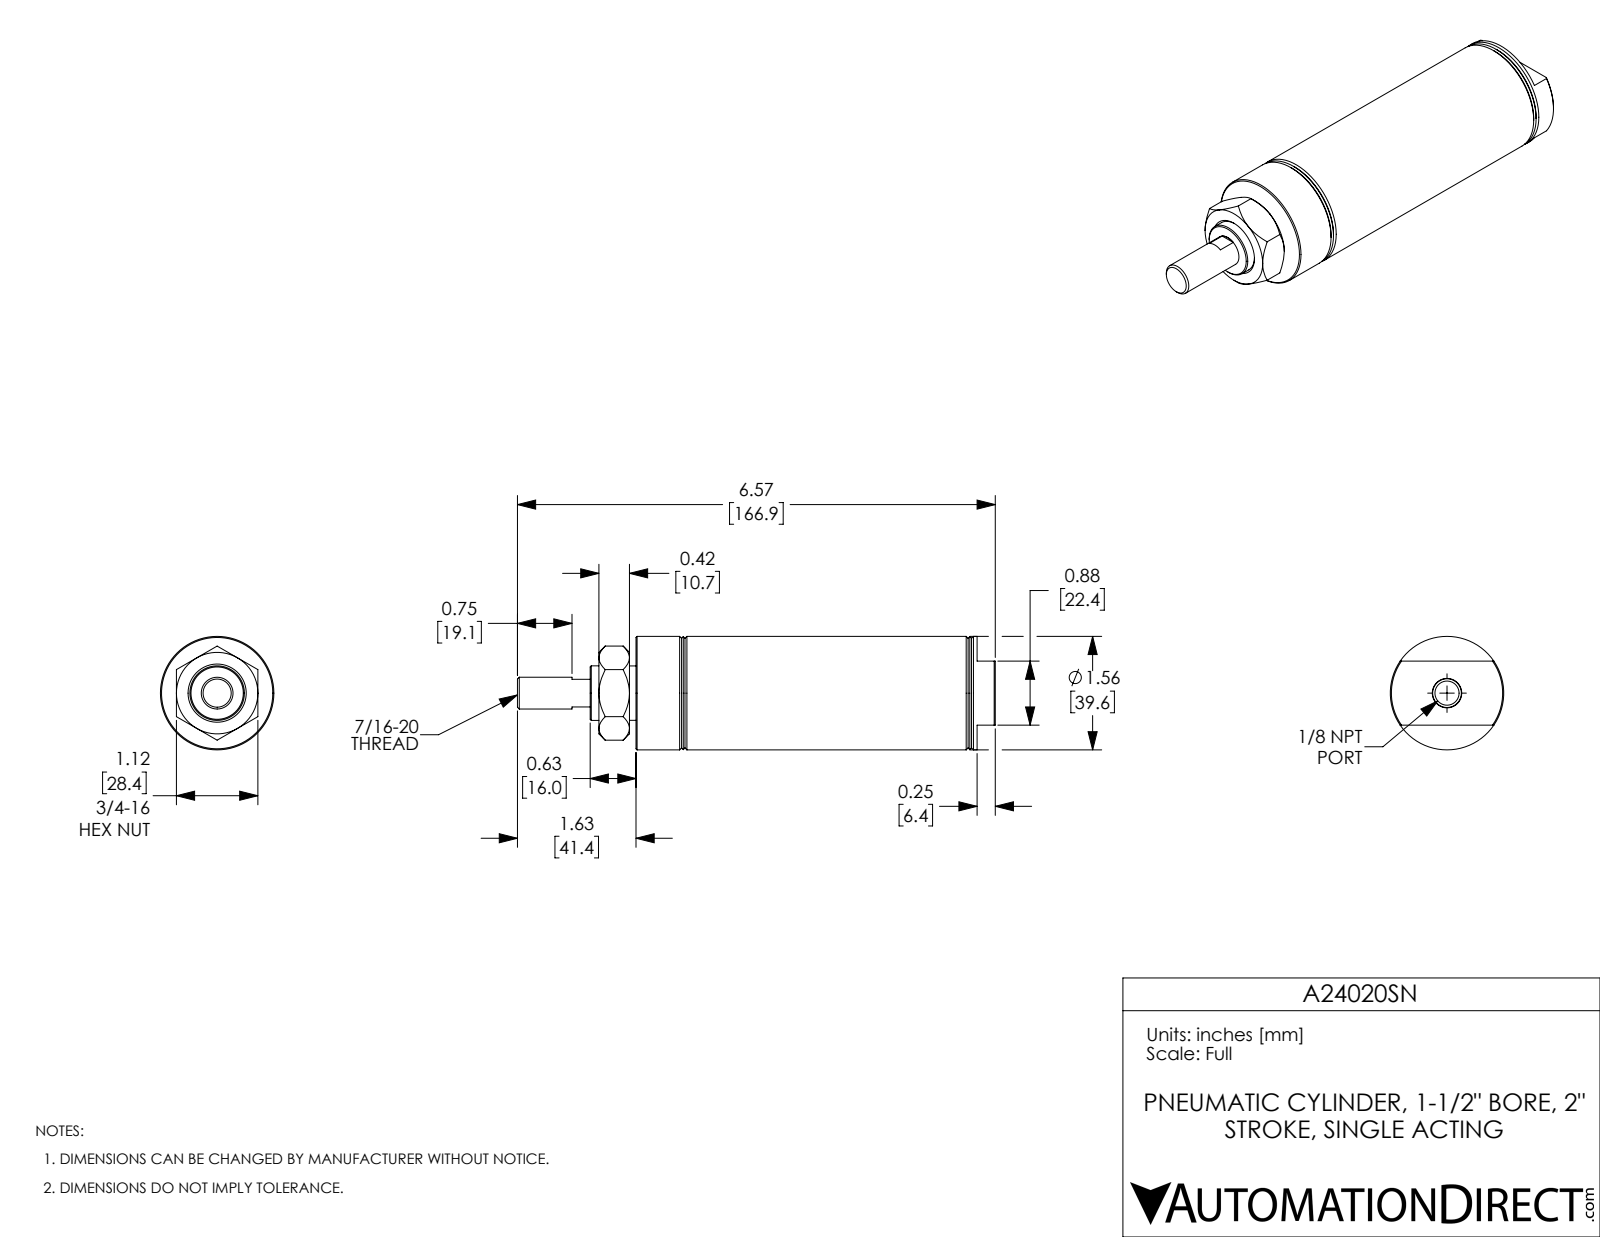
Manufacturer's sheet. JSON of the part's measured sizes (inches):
{"part_name": "A24020SN; A24020SN_Mounting Nut_D-3556; A24020SN-Rod; A24020SN-MainBody", "step_written_by": "SolidWorks 2017 (AUTOMOTIVE_DESIGN)", "units": "inches", "bodies": {"solids": 3, "faces": 93, "planar": 28, "cylindrical": 22, "other": 43}, "overall_size": [6.57, 1.56, 1.56], "volume_in3": 6.617, "surface_area_in2": 64.63, "round_holes": [[0.332, 1], [0.437, 1], [0.75, 1], [1.5, 1]], "round_bosses_or_shafts": [[1.56, 1], [0.747, 1]], "face_to_face_distances": [1.22, 3.72, 0.5, 2.5, 2, 3.22, 1.72, 4.94, 0.25, 1.12]}
